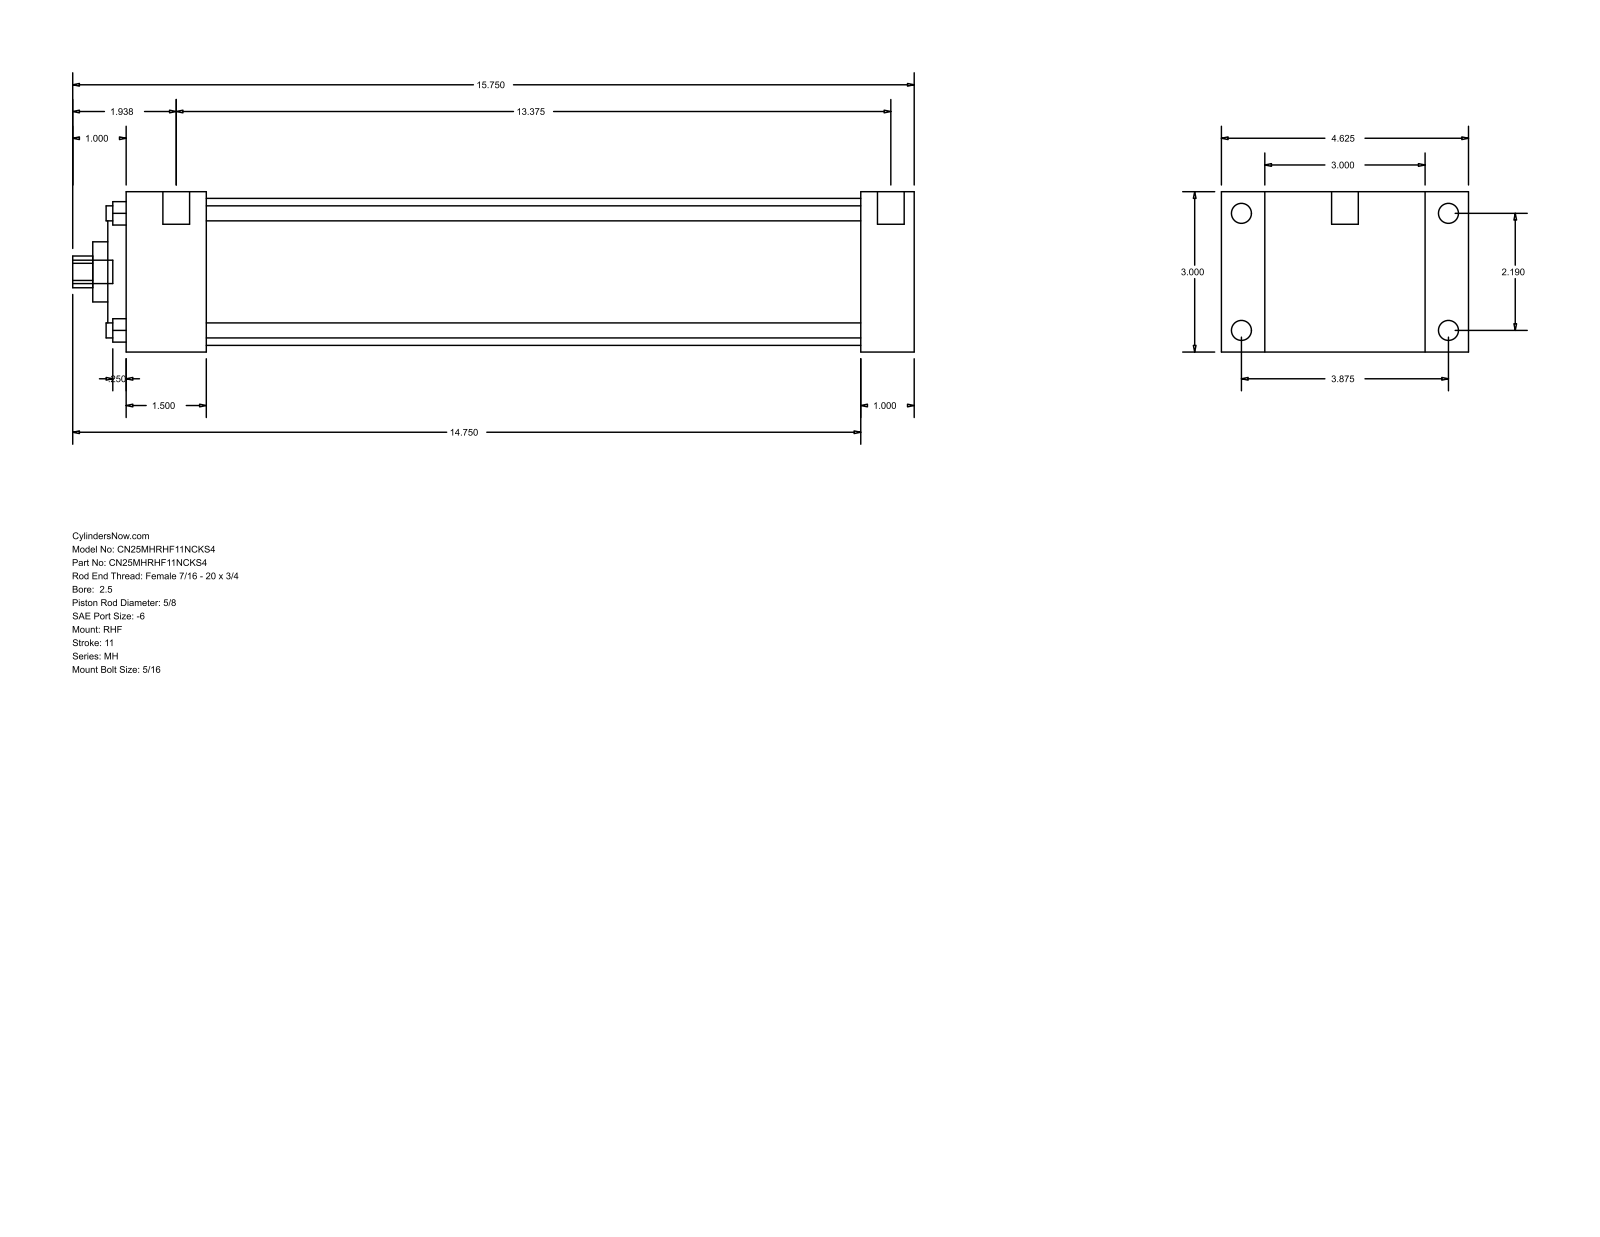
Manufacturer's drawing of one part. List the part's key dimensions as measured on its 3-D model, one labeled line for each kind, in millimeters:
Part name (STEP PRODUCT): MH_RHF__0250_0.625
STEP written by: GSSL Pune (CONFIG_CONTROL_DESIGN)
Units: millimetres
Bodies: 0 solids, 90 faces (61 planar, 29 cylindrical, 0 other)
Overall size (bounding box): 400.05 × 117.47 × 76.2
Round holes (diameter × count): ⌀7.14 ×4, ⌀15.88 ×1, ⌀28.57 ×1, ⌀55.55 ×1, ⌀69.85 ×1
Round bosses / shafts (diameter × count): ⌀9.53 ×4, ⌀5.56 ×4, ⌀12.7 ×2, ⌀11.11 ×1
Partial cylindrical surfaces — rounded edges, fillets, slot ends (radius × count): R7.54 ×1
Main face-to-face distances: 76.2, 25.4, 20.64, 96.84, 374.65, 349.25, 117.48, 38.1, 311.15, 336.55
Hole centre spacings: 39.33, 55.62, 78.66
